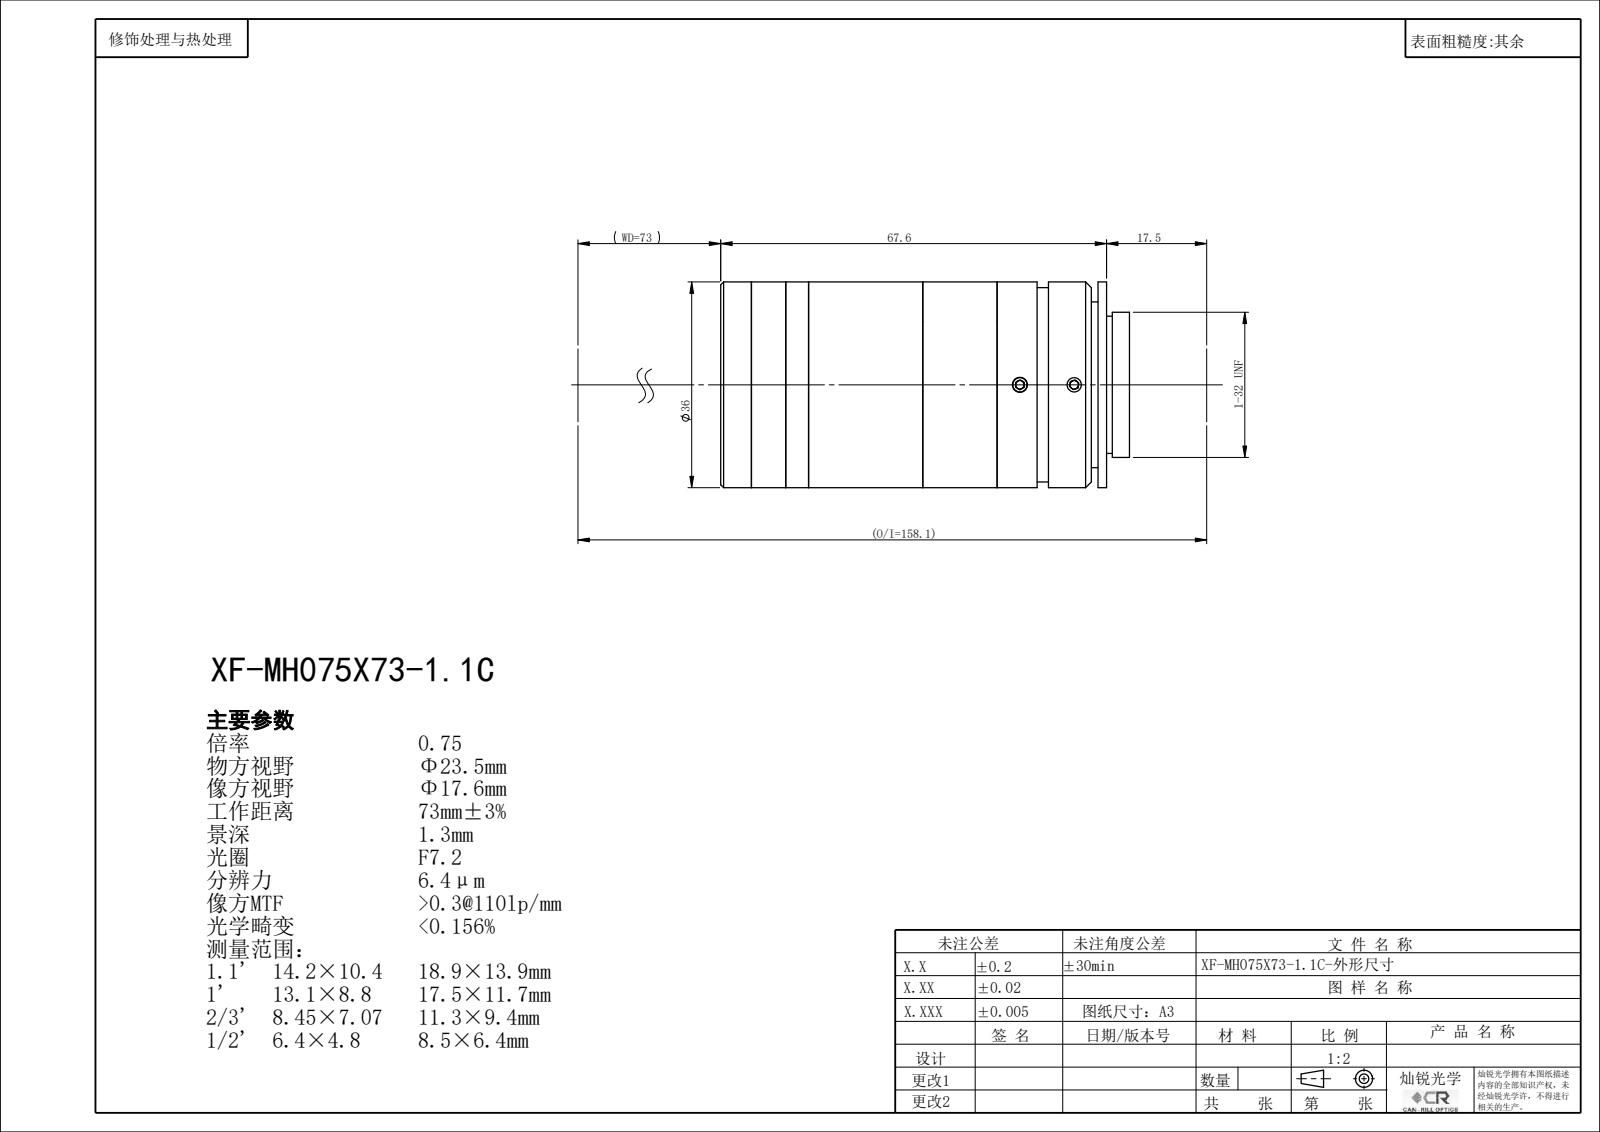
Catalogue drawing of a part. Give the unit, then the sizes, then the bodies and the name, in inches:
Units: inches
Overall size (bounding box): 2.817 × 1.417 × 1.417
Round holes (diameter × count): ⌀0.098 ×3, ⌀0.591 ×1, ⌀0.685 ×1, ⌀0.882 ×1, ⌀0.945 ×1, ⌀0.98 ×1, ⌀1.024 ×1, ⌀1.039 ×1
Round bosses / shafts (diameter × count): ⌀1.417 ×1, ⌀1.339 ×1, ⌀1 ×1
Main face-to-face distances: 0.755, 1.905, 2.659, 0.787, 0.059, 2.6, 0.696, 0.606, 1.299, 1.995
Bodies: 0 solids, 140 faces (72 planar, 42 cylindrical, 26 other)
Part name (STEP PRODUCT): XF-MH075X73-1.1C
STEP written by: SolidWorks 2022 (CONFIG_CONTROL_DESIGN)
